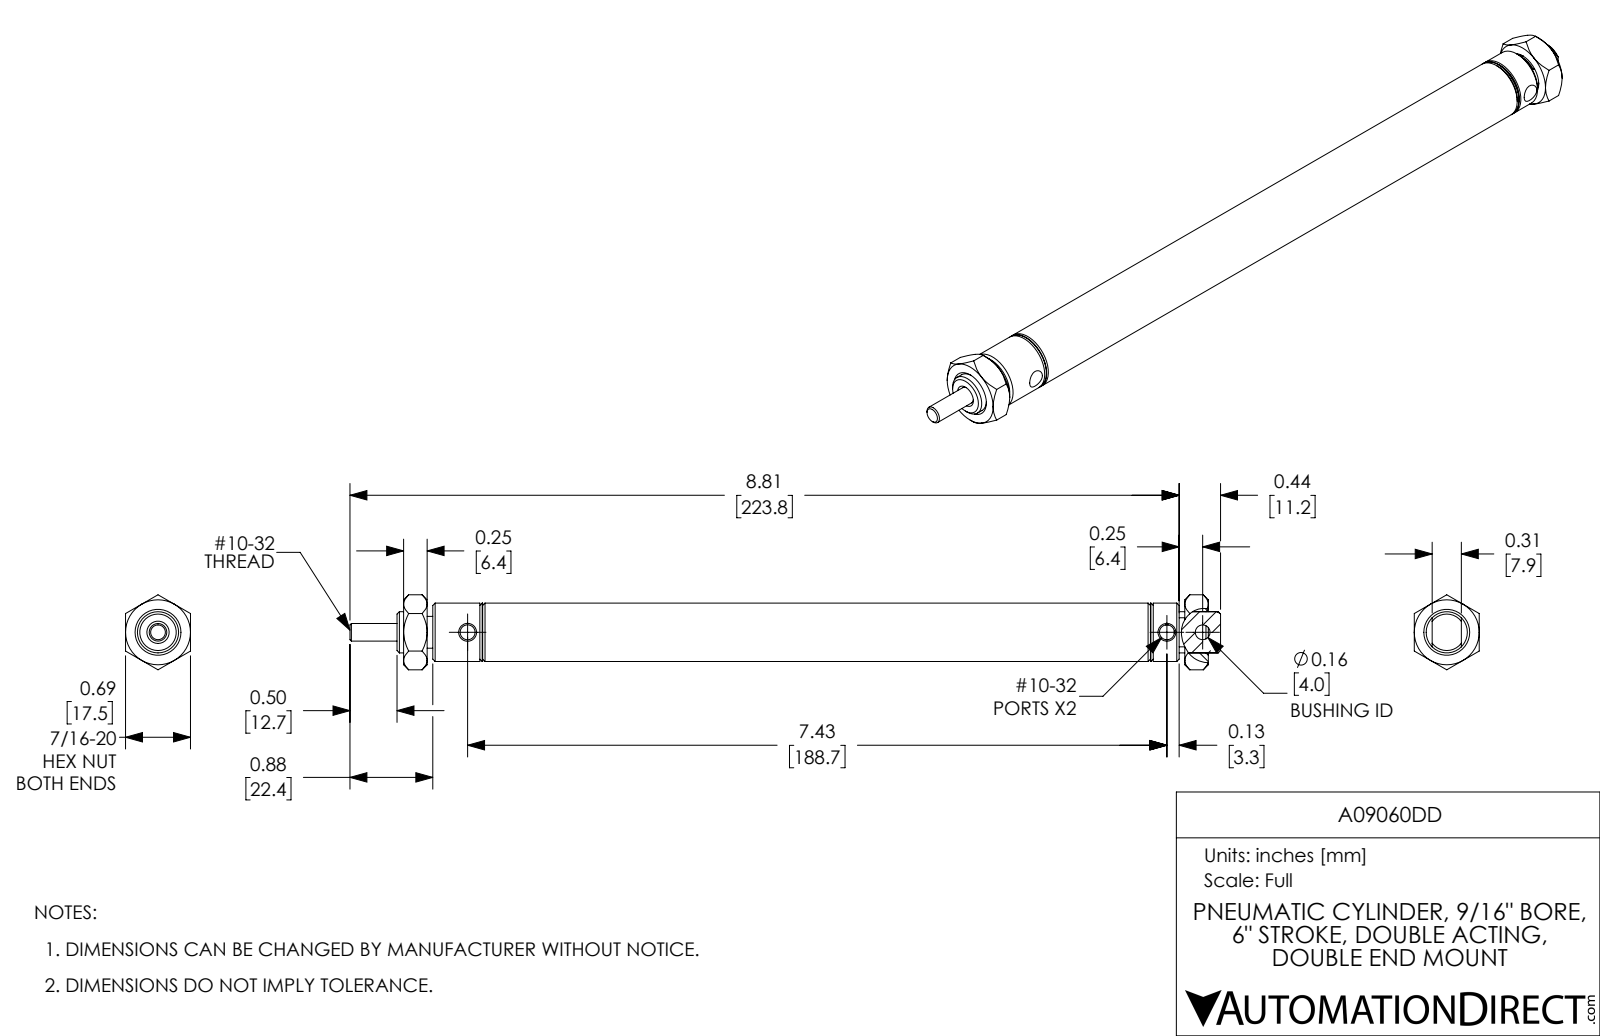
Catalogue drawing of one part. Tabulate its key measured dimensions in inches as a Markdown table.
| quantity | value |
| --- | --- |
| part name | A09060DD-Rod; A09060DD; A09060DD-MainBody; A09060DD_Mounting Nut_D-154 |
| STEP written by | SolidWorks 2017 (AUTOMOTIVE_DESIGN) |
| units | inches |
| bodies | 4 solids, 151 faces (36 planar, 46 cylindrical, 69 other) |
| overall size | 9.25 × 0.797 × 0.69 |
| volume | 1.28 in³ |
| surface area | 39.15 in² |
| round holes (diameter × count) | 0.159 × 2, 0.19 × 2, 0.156 × 1, 0.157 × 1, 0.187 × 1, 0.563 × 1 |
| round bosses / shafts (diameter × count) | 0.62 × 1, 0.437 × 1, 0.338 × 1 |
| main face-to-face distances | 0.69, 0.5, 0.25, 8.3, 0.715, 7.215, 7.275, 0.31, 6.5, 0.775 |
| hole center spacings | 0.38, 7.43, 7.81 |
